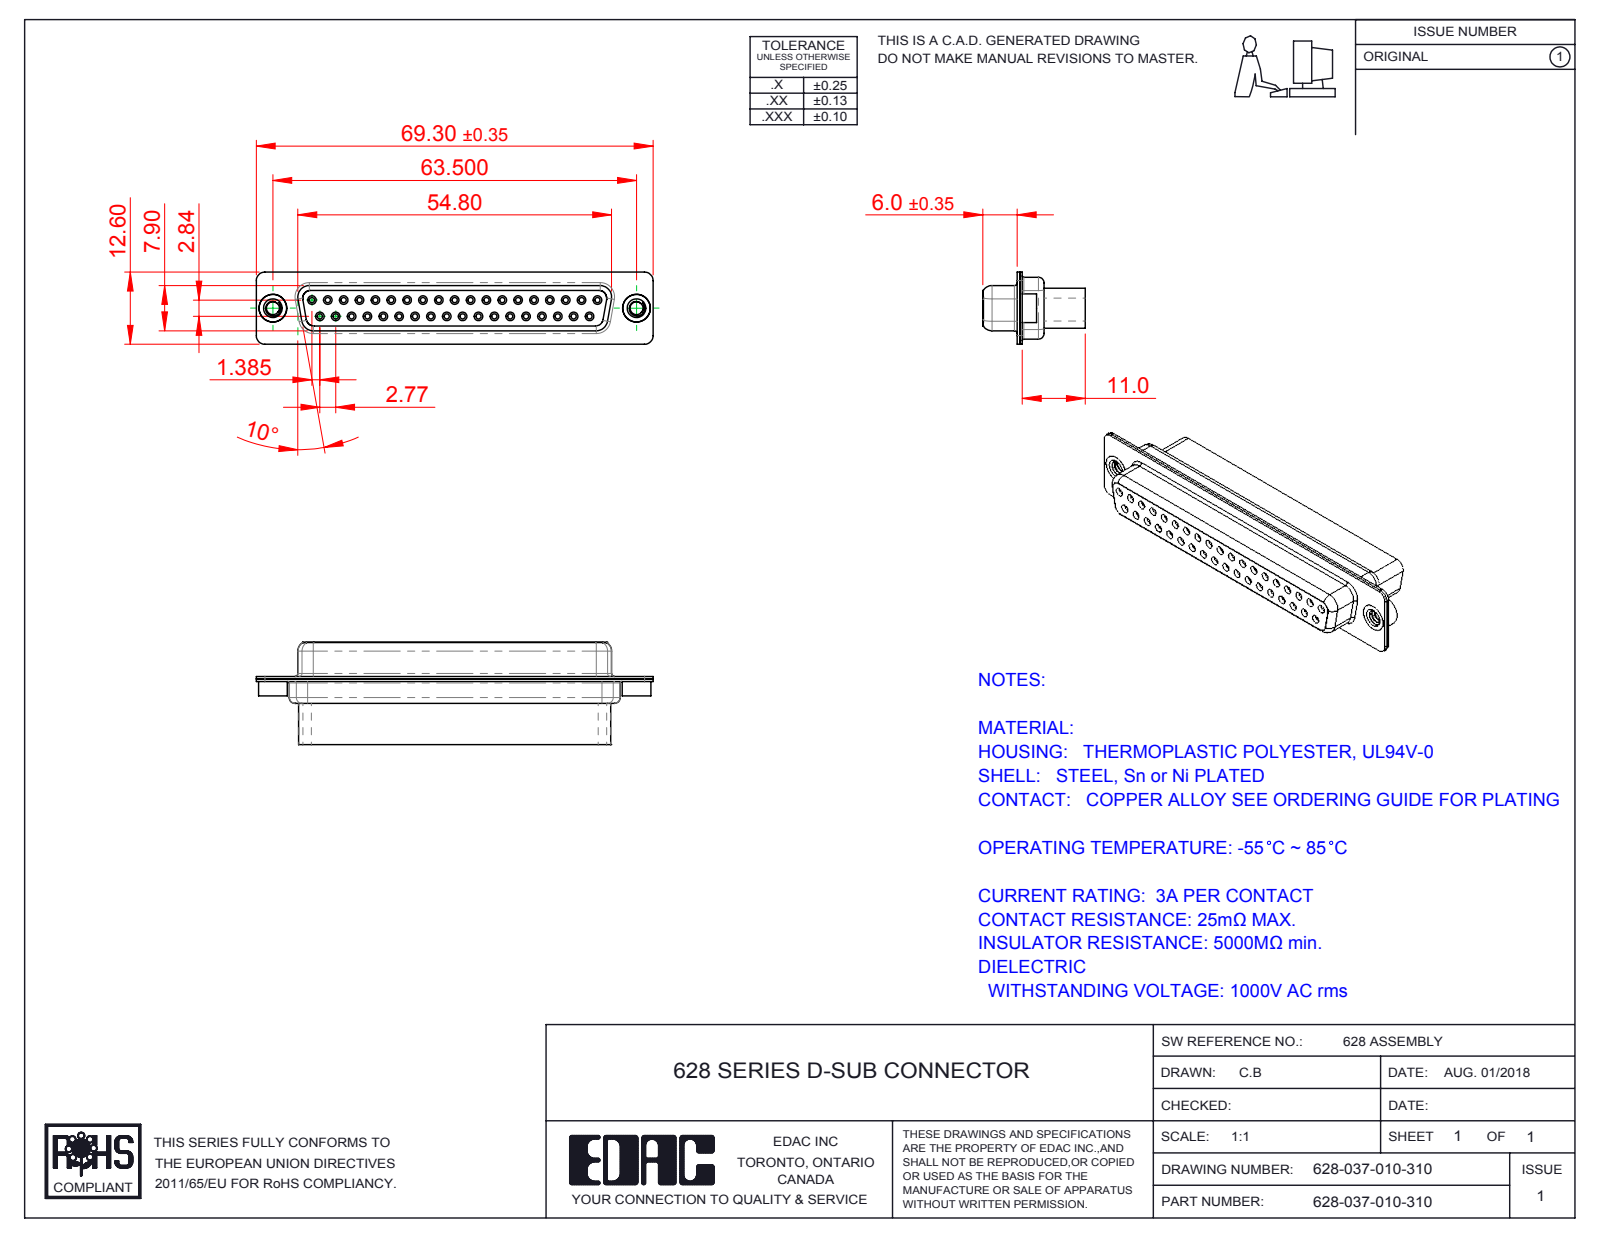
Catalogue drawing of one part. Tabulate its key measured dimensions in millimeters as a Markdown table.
| quantity | value |
| --- | --- |
| part name | 628 Shell Rear_37 Contacts; 628 Shell Front_37 Contacts; 628 Housing_37 HP; 628-050-010-310 (+1 more) |
| STEP written by | SolidWorks 2016 (CONFIG_CONTROL_DESIGN) |
| units | millimeters |
| bodies | 5 solids, 756 faces (178 planar, 431 cylindrical, 147 other) |
| overall size | 69.3 × 17.9 × 12.6 |
| volume | 6 660 mm³ |
| surface area | 10 943 mm² |
| round holes (diameter × count) | 0.9 × 37, 1.5 × 37, 2 × 37, 1.7 × 19, 1.6 × 18, 2.26 × 2, 4 × 2, 4.05 × 2, 4.85 × 2 |
| round bosses / shafts (diameter × count) | 5 × 2, 4.95 × 2, 4.8 × 2 |
| partial cylindrical surfaces (radius × count) | 1.5 × 16, 2 × 12, 0.25 × 4, 0.5 × 4, 0.6 × 4, 0.65 × 4, 0.95 × 4, 1 × 4 |
| main face-to-face distances | 0.4, 0.45, 6.6, 7, 1.9, 8.5, 0.85, 7.05, 7.45, 1.4 |
| hole center spacings | 3.16, 2.77, 5.54, 8.31, 5.04, 7.49, 11.08, 13.85 |
